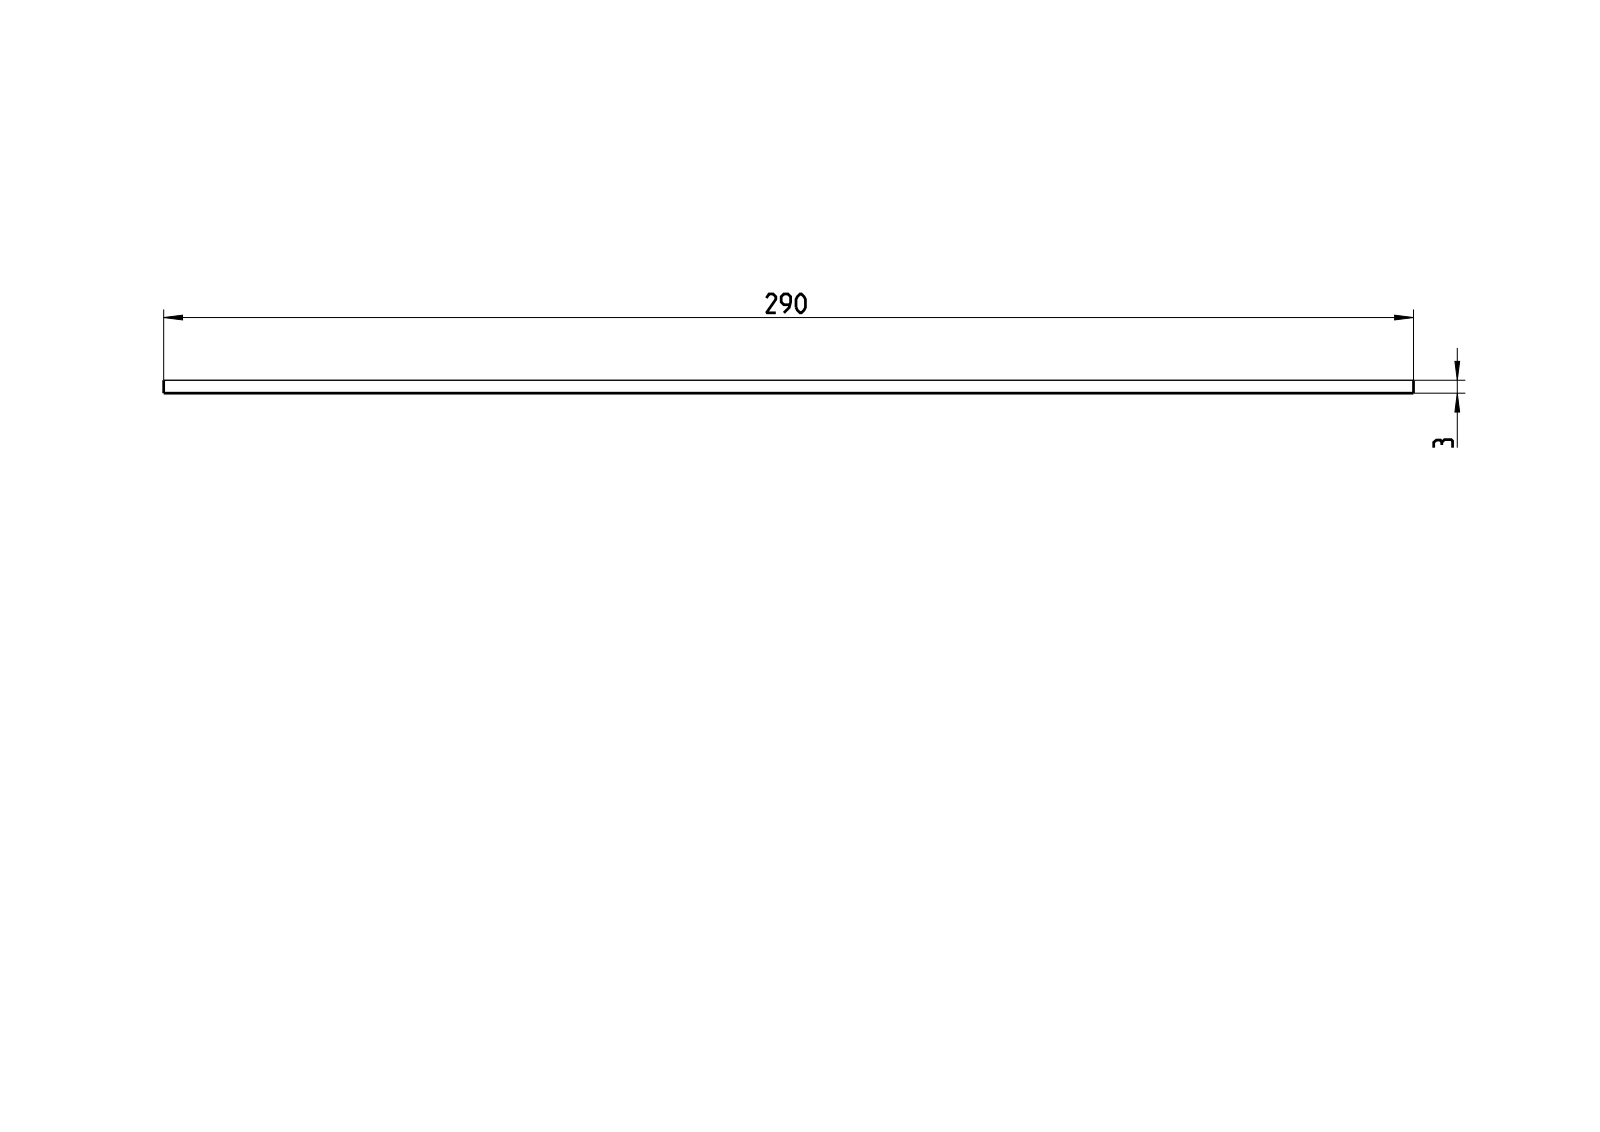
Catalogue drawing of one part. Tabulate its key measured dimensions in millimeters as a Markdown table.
| quantity | value |
| --- | --- |
| part name | T-01186; BKG3002BL2_ASM |
| STEP written by | CREO PARAMETRIC BY PTC INC, 2022024 (AUTOMOTIVE_DESIGN) |
| units | millimeters |
| bodies | 1 solid, 6 faces (6 planar, 0 cylindrical, 0 other) |
| overall size | 999 × 290 × 3 |
| volume | 869 130 mm³ |
| surface area | 587 154 mm² |
| main face-to-face distances | 3, 290, 999 |
